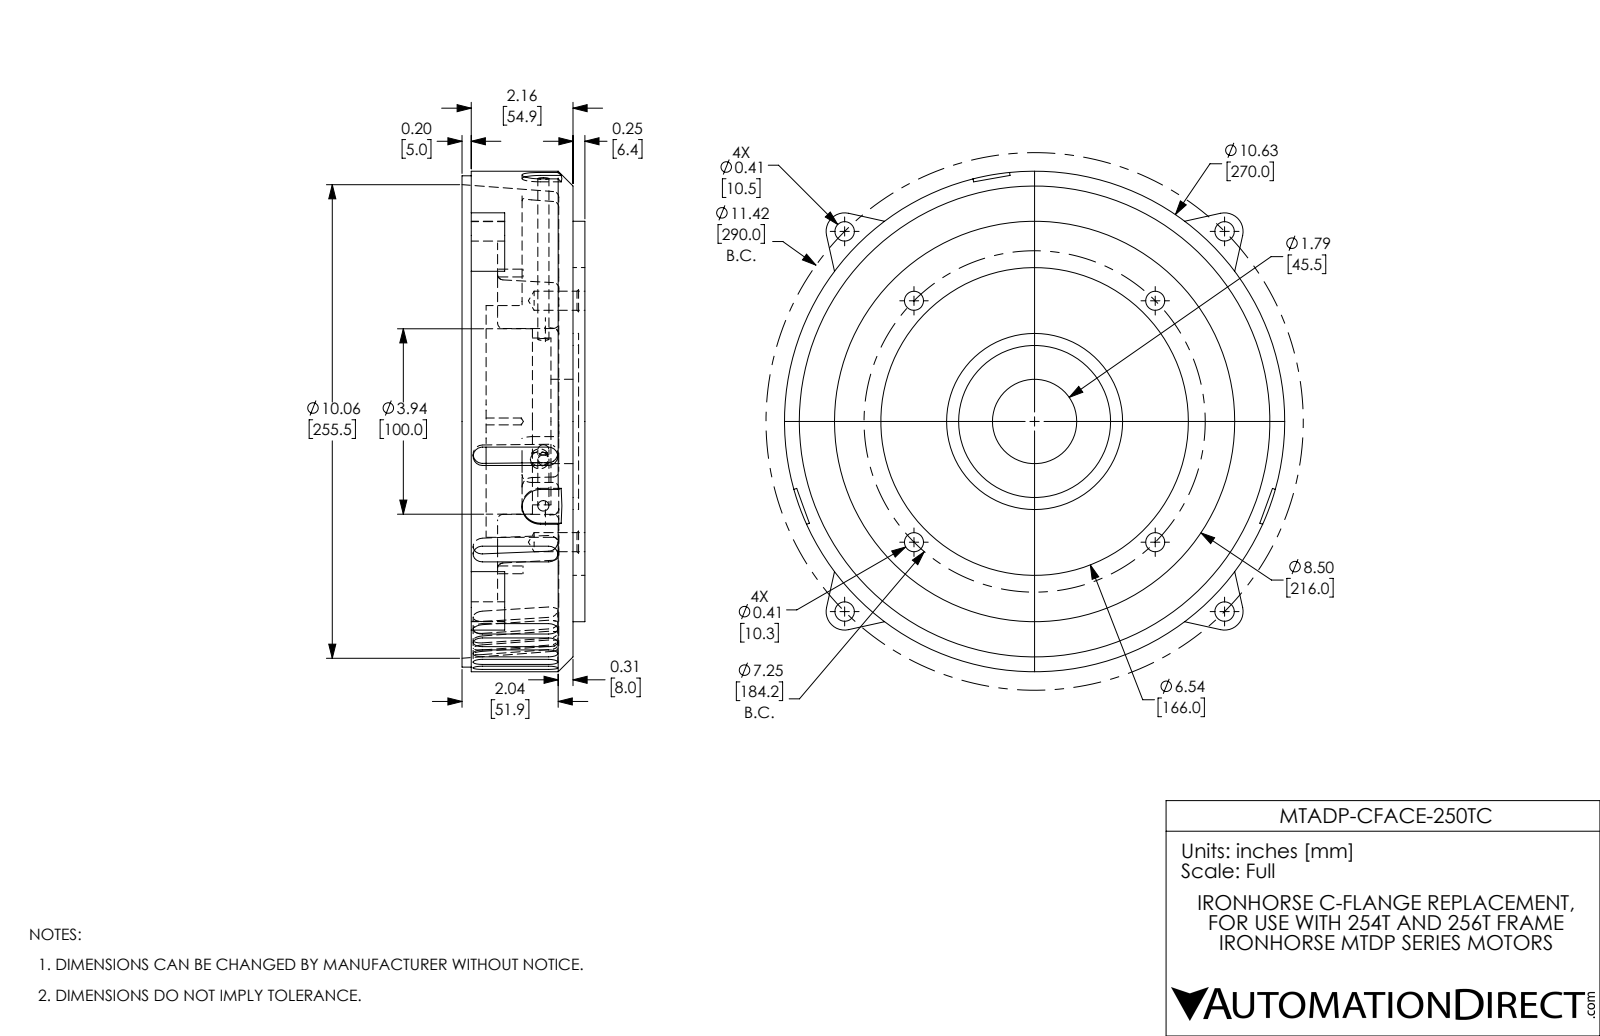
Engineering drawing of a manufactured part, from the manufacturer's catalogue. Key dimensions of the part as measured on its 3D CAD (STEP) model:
Part name (STEP PRODUCT): MTADP-CFACE-250
STEP written by: SolidWorks 2017 (AUTOMOTIVE_DESIGN)
Units: inches
Bodies: 1 solid, 483 faces (110 planar, 192 cylindrical, 181 other)
Overall size (bounding box): 10.63 × 10.63 × 2.612
Volume: 81.16 in³ · Surface area: 408.2 in²
Round holes (diameter × count): ⌀0.165 ×4, ⌀0.406 ×4, ⌀0.413 ×4, ⌀0.236 ×3, ⌀0.146 ×2, ⌀0.394 ×1, ⌀1.791 ×1, ⌀3.228 ×1, ⌀3.543 ×1, ⌀3.937 ×1, ⌀6.535 ×1
Round bosses / shafts (diameter × count): ⌀10.63 ×1, ⌀10.433 ×1, ⌀8.504 ×1, ⌀4.921 ×1, ⌀3.74 ×1
Partial cylindrical surfaces — rounded edges, fillets, slot ends (radius × count): R0.118 ×58, R0.197 ×38, R0.394 ×7, R0.591 ×4, R0.276 ×2
Main face-to-face distances: 0.304, 0.557, 0.254, 1.299, 0.559, 0.165, 0.469, 0.722, 1.378, 1.543
Hole centre spacings: 5.745, 6.763, 7.242, 0.831, 1.252, 2.083, 2.571, 3.248
